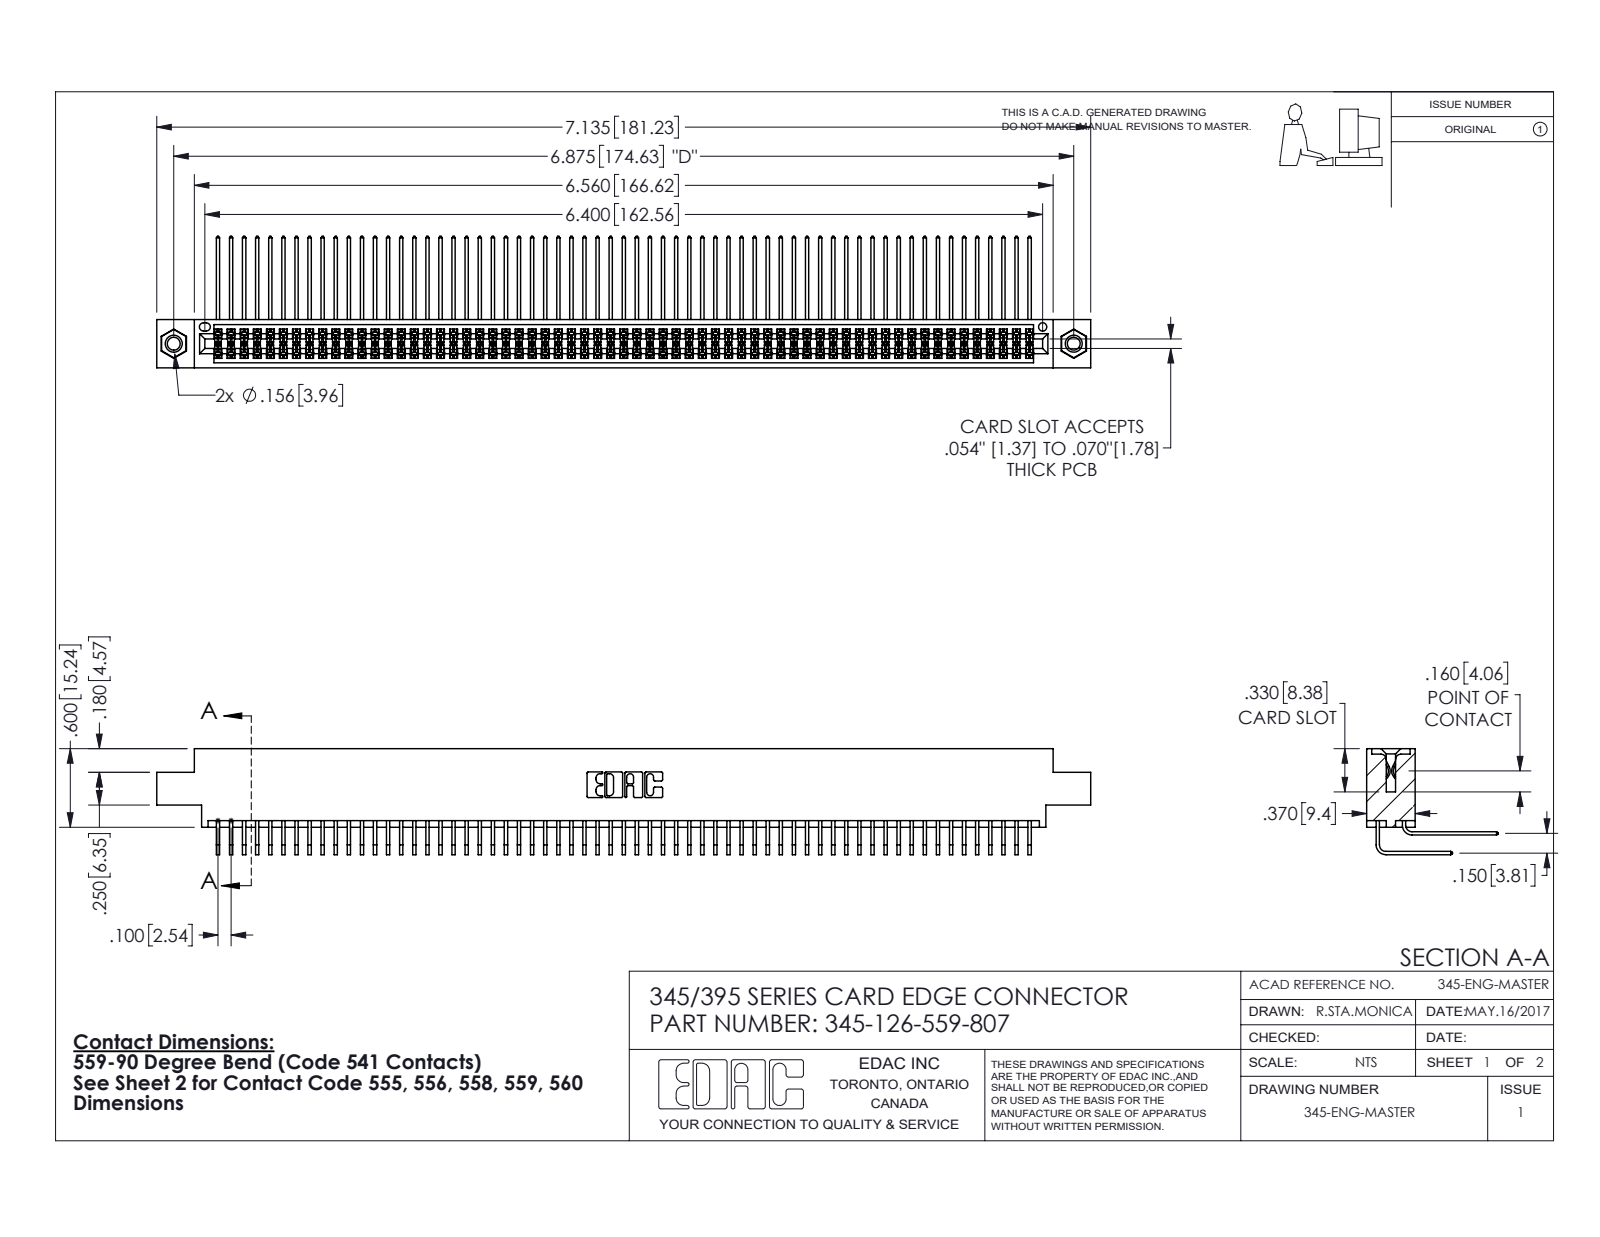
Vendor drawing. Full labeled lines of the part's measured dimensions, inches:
Part name (STEP PRODUCT): 345-292-001_559 Tail - 2; 345-292-001_558 559 Tail - 1; 345-126-559-807; 345-250-001_345-250-005-103 (+1 more)
STEP written by: SolidWorks 2016 (CONFIG_CONTROL_DESIGN)
Units: inches
Bodies: 129 solids, 6742 faces (4526 planar, 2200 cylindrical, 16 other)
Overall size (bounding box): 7.135 × 1.005 × 0.809
Volume: 1.123 in³ · Surface area: 48.35 in²
Round holes (diameter × count): ⌀0.098 ×2, ⌀0.125 ×2, ⌀0.156 ×2, ⌀0.064 ×1
Round bosses / shafts (diameter × count): ⌀0.155 ×2
Partial cylindrical surfaces — rounded edges, fillets, slot ends (radius × count): R0.006 ×251, R0.01 ×22, R0.007 ×6, R0.031 ×6, R0.026 ×3, R0.014 ×2, R0.019 ×2, R0.022 ×2
Main face-to-face distances: 0.072, 0.298, 0.2, 0.37, 0.098, 0.272, 0.025, 0.225, 0.175, 0.15
Hole centre spacings: 0.27, 6.639, 6.875
